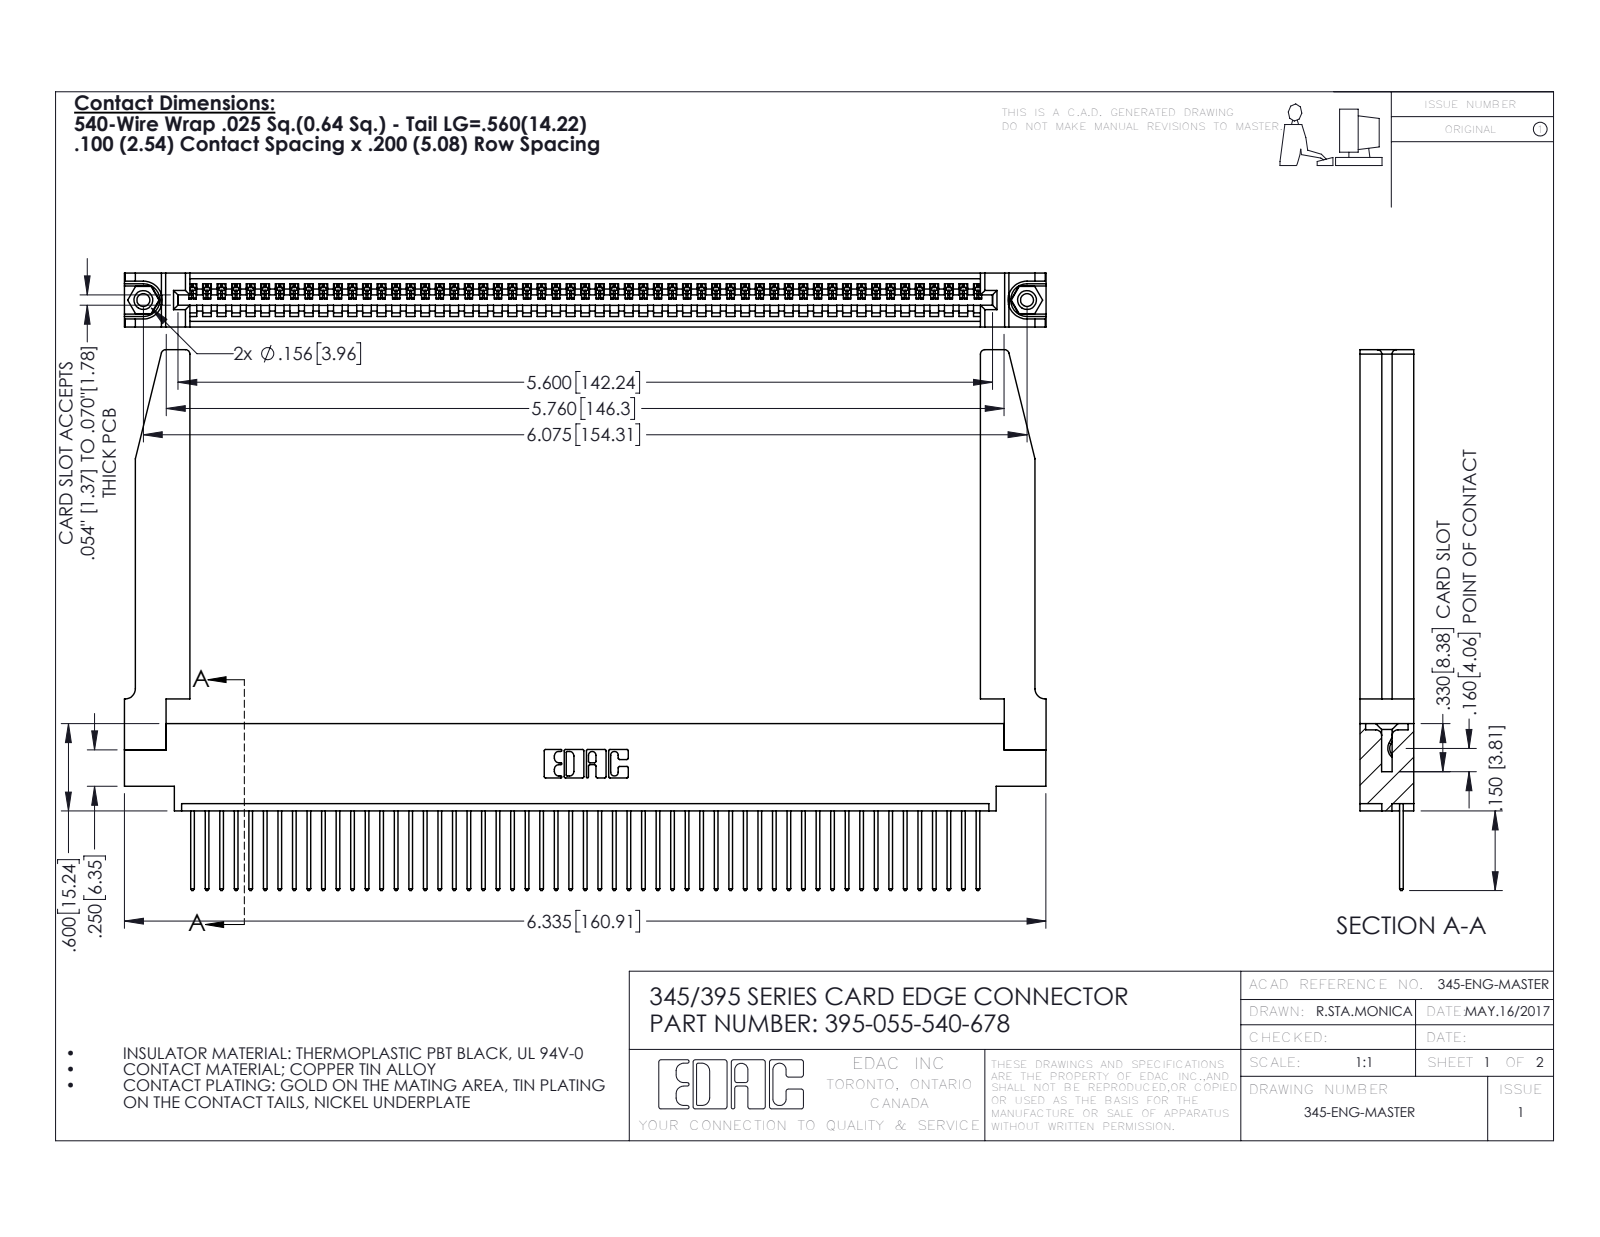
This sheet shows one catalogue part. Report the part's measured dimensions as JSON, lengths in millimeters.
{"part_name": "345-220-078_345-220-078; 345-250-001_345-250-001-102; 345 Part_0.170 Offset - 0.156 Dia-TH; 345-292-001_345-293-140 (+1 more)", "step_written_by": "SolidWorks 2016 (CONFIG_CONTROL_DESIGN)", "units": "millimeters", "bodies": {"solids": 60, "faces": 3554, "planar": 2426, "cylindrical": 1076, "other": 52}, "overall_size": [160.9, 94.4, 9.4], "volume_mm3": 23120, "surface_area_mm2": 28090, "round_holes": [[2.3, 2], [3.2, 2], [4, 2], [1.6, 1]], "round_bosses_or_shafts": [[3.9, 2]], "partial_cylinders_radius": [[0.2, 110], [0.3, 110], [0.3, 22], [0.8, 8], [0.2, 6], [0.8, 6], [0.7, 3], [0.8, 2]], "face_to_face_distances": [1.8, 9.4, 7.6, 2.5, 6.9, 0.6, 5.1, 5.7, 3.8, 3.8], "hole_center_spacings": [6.9, 148.3, 154.3]}
